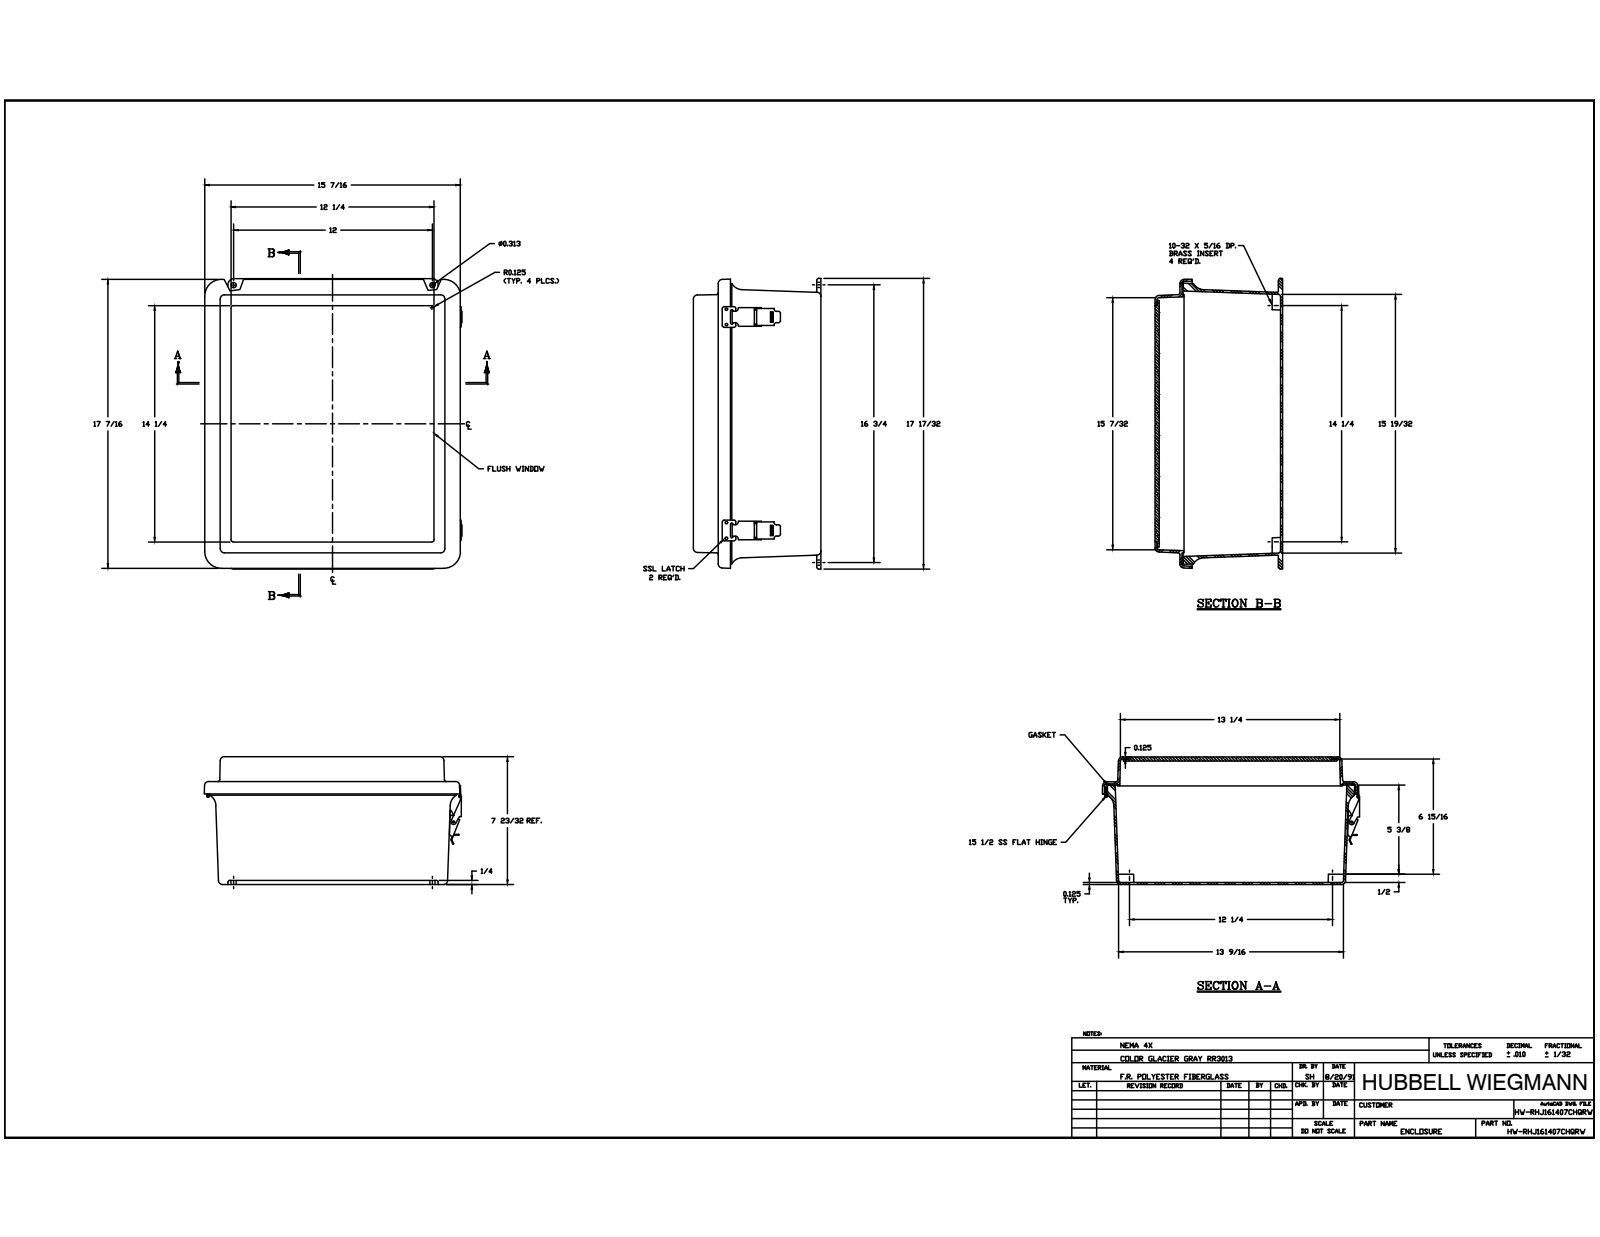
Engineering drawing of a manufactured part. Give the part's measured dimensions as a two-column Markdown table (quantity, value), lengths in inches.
| quantity | value |
| --- | --- |
| part name | J1614HL_8; RMINS45821P_163; RMINS45821P_164; RMINS45821P_165 (+8 more) |
| STEP written by | Autodesk Inventor 2014 (AUTOMOTIVE_DESIGN) |
| units | inches |
| bodies | 41 solids, 1180 faces (519 planar, 488 cylindrical, 173 other) |
| overall size | 17.531 × 15.566 × 7.697 |
| volume | 171.4 in³ |
| surface area | 2 187 in² |
| round holes (diameter × count) | 0.14 × 22, 0.131 × 10, 0.104 × 8, 0.152 × 8, 0.13 × 4, 0.156 × 4, 0.218 × 4, 0.135 × 2, 0.375 × 2, 0.085 × 1 |
| round bosses / shafts (diameter × count) | 0.125 × 18, 0.25 × 10, 0.27 × 4, 0.3 × 1, 0.17 × 1, 0.155 × 1, 0.12 × 1 |
| partial cylindrical surfaces (radius × count) | 0.125 × 32, 0.015 × 20, 0.031 × 20, 0.25 × 20, 0.045 × 16, 0.03 × 12, 0.022 × 9, 0.06 × 6 |
| main face-to-face distances | 0.125, 7.447, 0.125, 0.25, 7.697, 7.572, 7.322, 5.945, 1.502, 6.07 |
| hole center spacings | 3.75, 7.5, 12.869, 0.937, 12.868, 0.25, 0.75, 11.25 |
